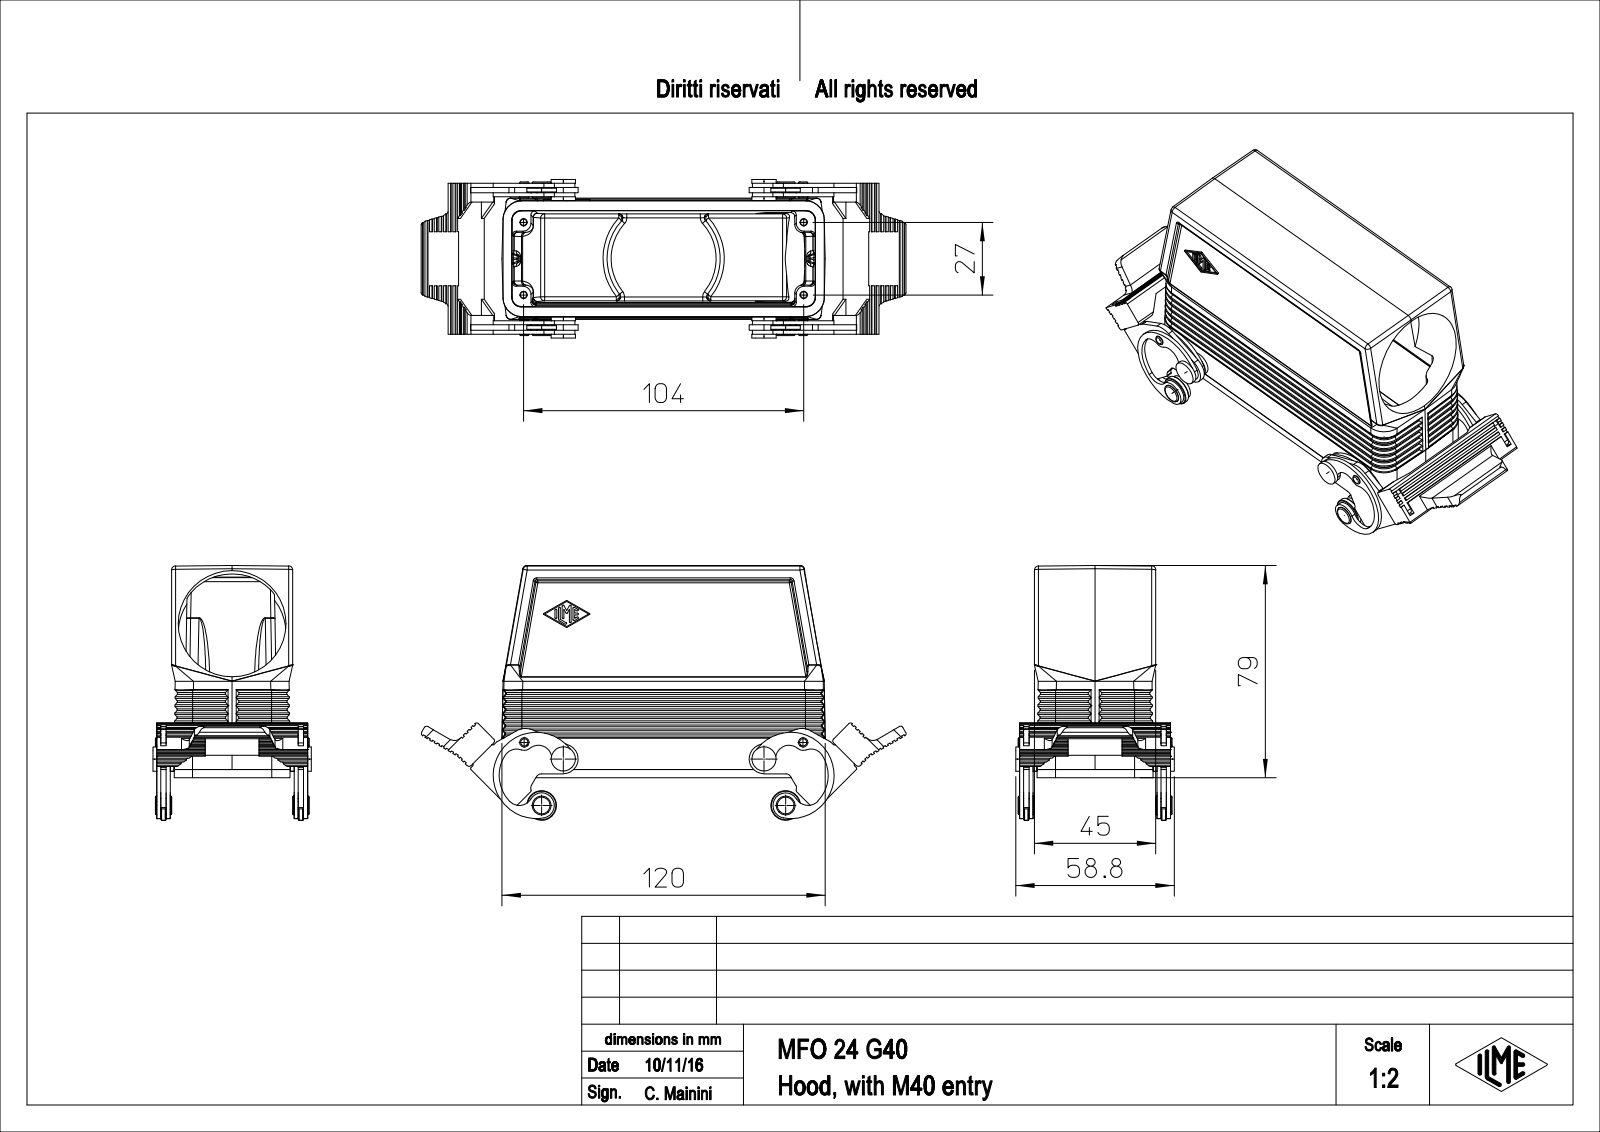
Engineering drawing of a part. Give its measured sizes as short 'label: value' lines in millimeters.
name: MFO_24_G40
written by: PTC Creo Elements/Direct Modeling 19.0E 27-Jun-2016 (C) Parametric Technology GmbH (AUTOMOTIVE_DESIGN)
unit: mm
bodies: 1 solid, 1268 faces (676 planar, 400 cylindrical, 192 other)
size: 179.97 × 94.54 × 58.8
volume: 136 373 mm³; area: 75 815 mm²
holes: 4× ⌀5, 2× ⌀3.1, 2× ⌀4, 1× ⌀40
bosses: 2× ⌀11, 2× ⌀9, 2× ⌀7, 2× ⌀4.8, 2× ⌀3.5, 2× ⌀3
rounds: 86× R0.5, 16× R1.5, 12× R3, 10× R1, 10× R7, 6× R5, 4× R2, 4× R3.5
face distances: 2, 1, 43, 3.5, 51, 4, 1.5, 6, 52.5, 54.5
hole spacings: 19, 19.11, 24.25, 34.07, 99.79, 118.28, 122.58, 15.74
